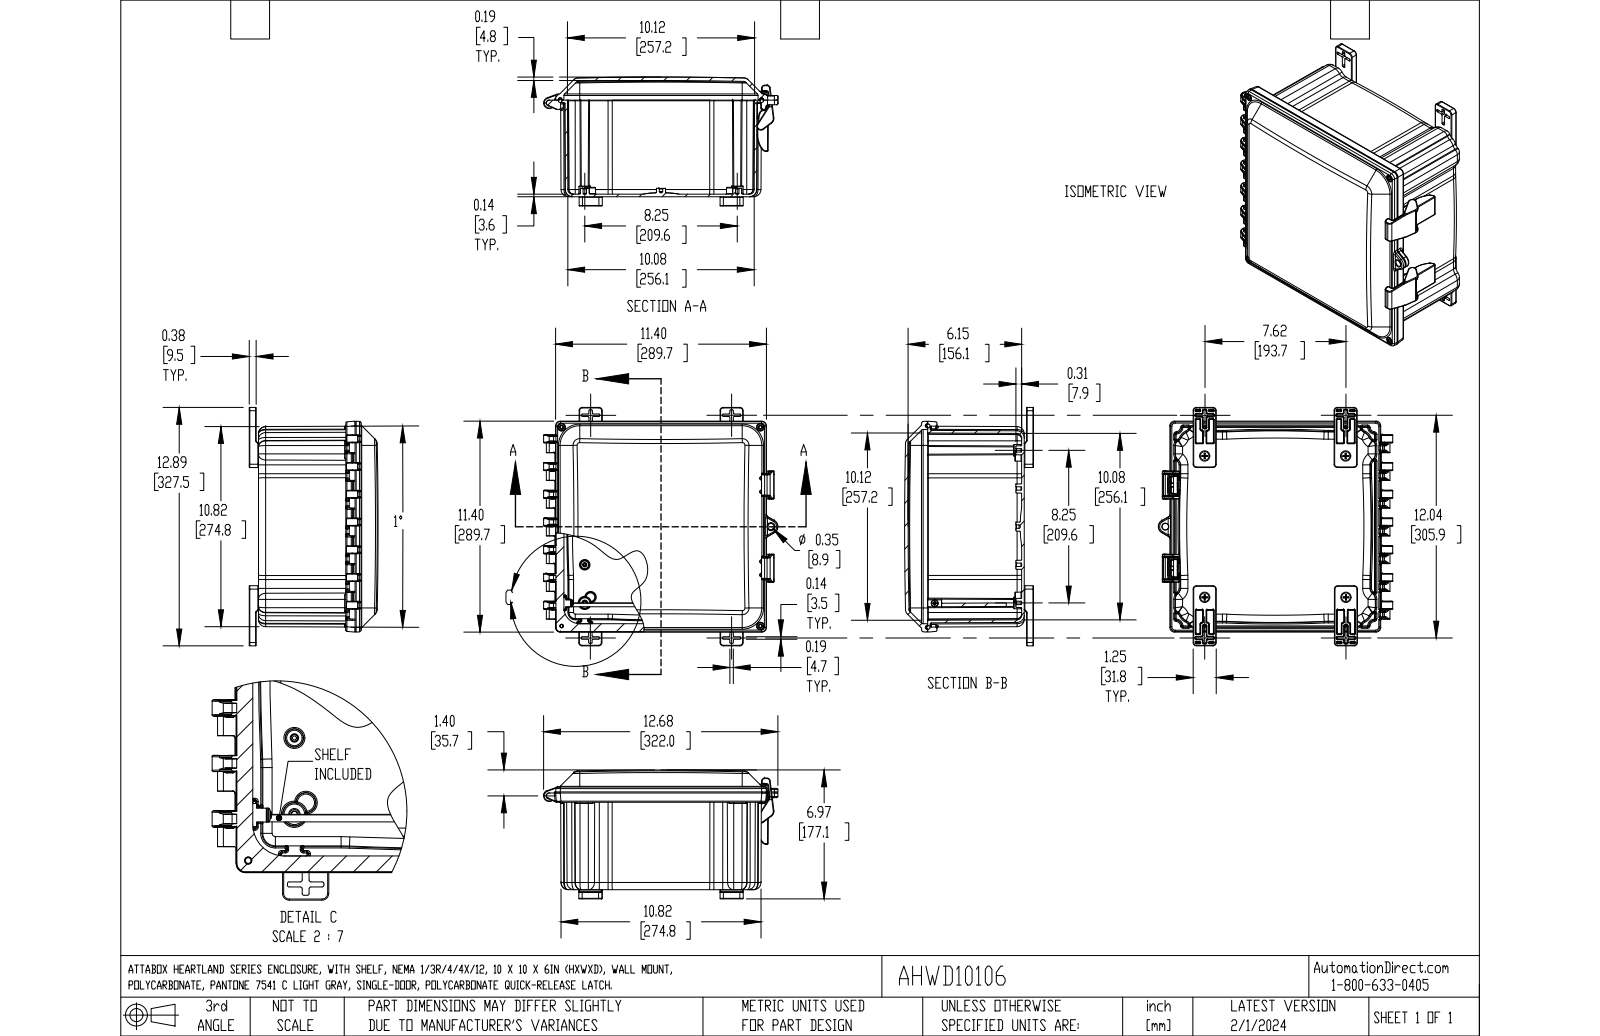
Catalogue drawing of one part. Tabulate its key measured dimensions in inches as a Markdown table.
| quantity | value |
| --- | --- |
| part name | AHWD10106 |
| STEP written by | SolidWorks 2023 (AUTOMOTIVE_DESIGN) |
| units | inches |
| bodies | 23 solids, 2025 faces (741 planar, 643 cylindrical, 641 other) |
| overall size | 12.892 × 12.676 × 6.973 |
| volume | 104.9 in³ |
| surface area | 1 252 in² |
| round holes (diameter × count) | 0.187 × 11, 0.156 × 8, 0.195 × 4, 0.196 × 4, 0.25 × 4, 0.265 × 4, 0.29 × 4, 0.39 × 4, 0.19 × 2, 0.327 × 1, 0.375 × 1, 0.45 × 1 |
| round bosses / shafts (diameter × count) | 0.487 × 11, 0.315 × 8, 0.625 × 4, 0.394 × 4, 0.25 × 4, 0.373 × 2, 0.2 × 2, 0.313 × 1 |
| partial cylindrical surfaces (radius × count) | 0.035 × 184, 0.05 × 52, 0.03 × 34, 0.065 × 27, 0.01 × 22, 0.02 × 21, 0.18 × 16, 0.334 × 16 |
| main face-to-face distances | 0.14, 0.119, 10.119, 5.225, 10.238, 5.085, 10, 10, 0.119, 0.19 |
| hole center spacings | 9.582, 10.75, 4.125, 5.833, 2.063, 8.504, 9.319, 10.061 |
